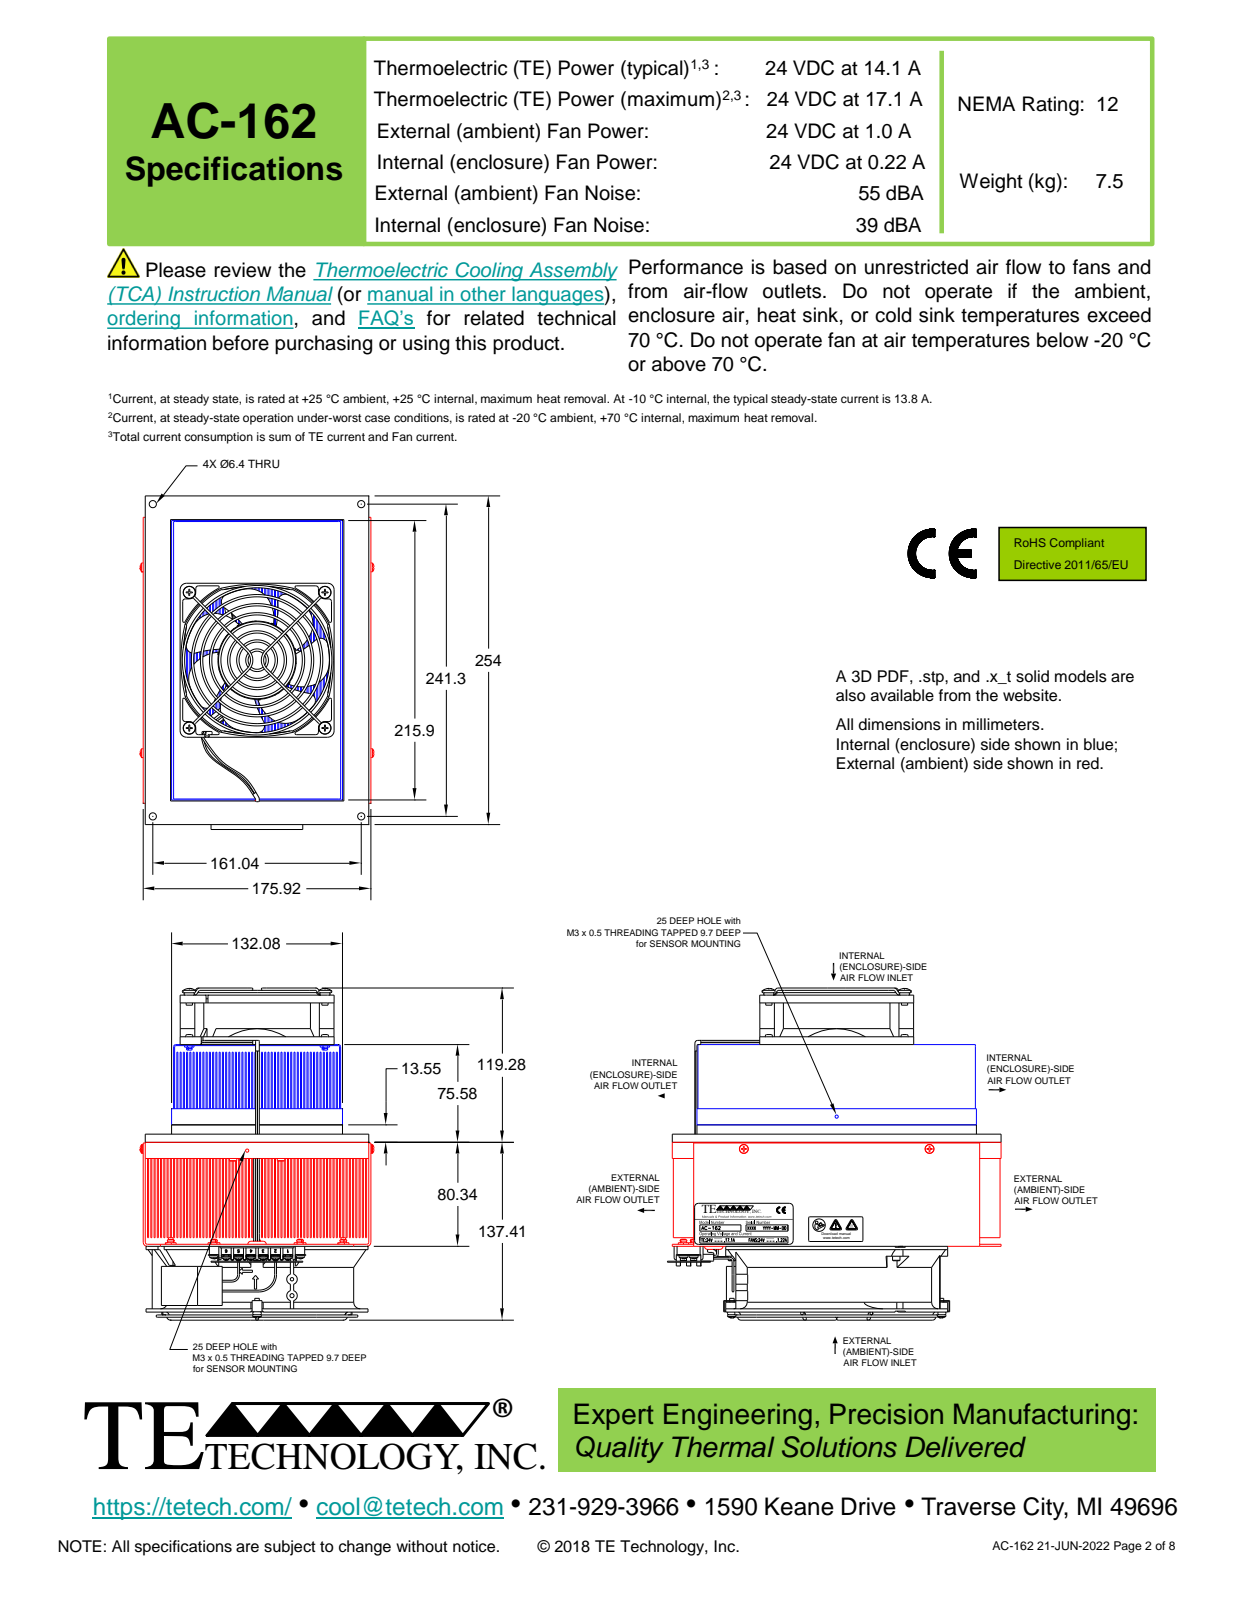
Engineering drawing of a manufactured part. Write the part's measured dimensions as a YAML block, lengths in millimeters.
part_name: "825-7521-001 heat sink assy; 2586 cold sink shroud; PEM LKS-440-2; 2586 cold sink shroud with PEMS (+8 more)"
step_written_by: "Alibre (AUTOMOTIVE_DESIGN)"
units: millimeters
bodies: {solids: 198, faces: 4844, planar: 2909, cylindrical: 822, other: 1113}
overall_size: [257.77, 256.69, 180.8]
volume: 3207000
surface_area: 3567000
round_holes:
  - {diameter: 2.64, count: 25}
  - {diameter: 2.65, count: 8}
  - {diameter: 4.17, count: 8}
  - {diameter: 4.22, count: 8}
  - {diameter: 4.27, count: 8}
  - {diameter: 4.83, count: 8}
  - {diameter: 5.56, count: 8}
  - {diameter: 5.84, count: 8}
  - {diameter: 12.7, count: 8}
  - {diameter: 1.91, count: 6}
  - {diameter: 3.53, count: 6}
  - {diameter: 3.94, count: 6}
round_bosses_or_shafts:
  - {diameter: 3.51, count: 31}
  - {diameter: 6.86, count: 22}
  - {diameter: 1.42, count: 20}
  - {diameter: 2.3, count: 16}
  - {diameter: 5.74, count: 11}
  - {diameter: 9.53, count: 9}
  - {diameter: 1.8, count: 9}
  - {diameter: 10.31, count: 8}
partial_cylinders:
  - {radius: 1, count: 44}
  - {radius: 0.5, count: 29}
  - {radius: 0.79, count: 24}
  - {radius: 0.95, count: 21}
  - {radius: 0.81, count: 14}
  - {radius: 0.78, count: 12}
  - {radius: 2, count: 12}
  - {radius: 0.38, count: 8}
face_to_face_distances: [5.03, 10.06, 2.51, 7.54, 2.52, 1.7, 6.73, 3.33, 0.81, 11.76]
hole_center_spacings: [19.05, 25.49, 37.08, 51.59, 65.63, 65.84, 75.38, 89.77]
